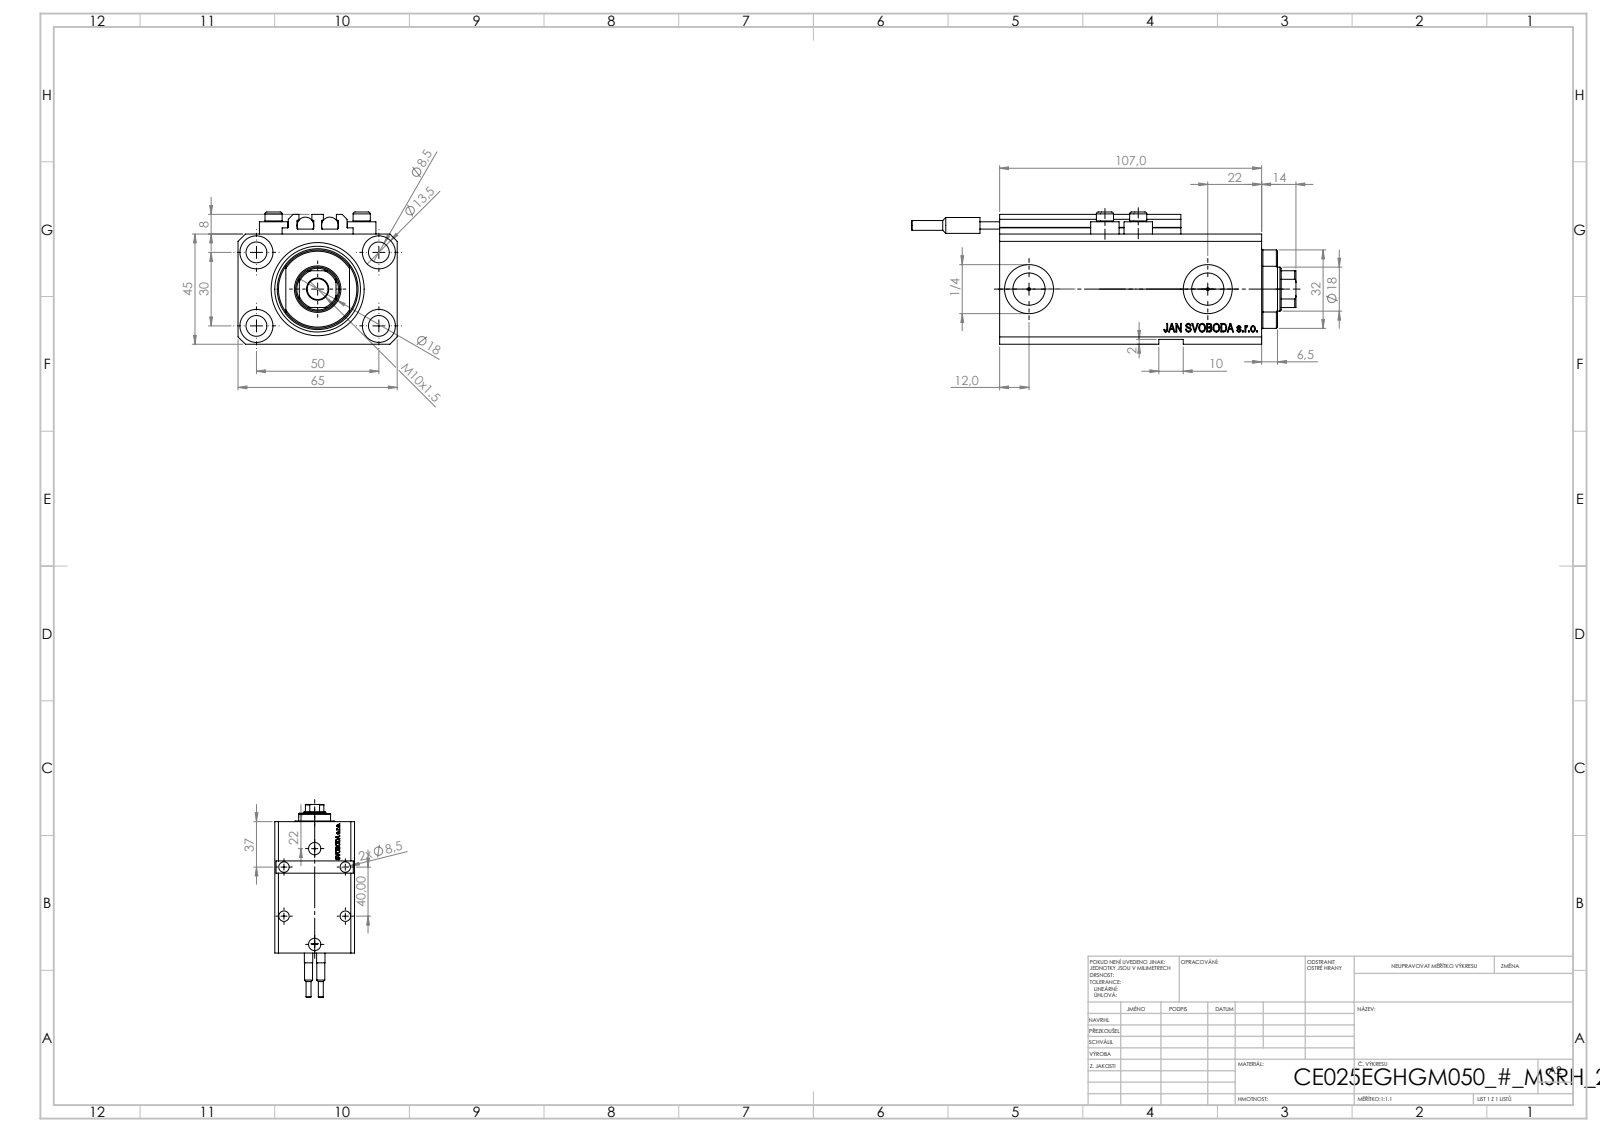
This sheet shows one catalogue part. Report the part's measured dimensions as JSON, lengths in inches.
{"part_name": "ALLEN BOLT V250CE; V250CE_C_VCP; SWITCH_V250CE; V250CE_VC_E (+1 more)", "step_written_by": "SolidWorks 2019 (CONFIG_CONTROL_DESIGN)", "units": "inches", "bodies": {"solids": 10, "faces": 1139, "planar": 543, "cylindrical": 158, "other": 438}, "overall_size": [6.181, 2.559, 2.126], "volume_in3": 16.9, "surface_area_in2": 123.4, "round_holes": [[0.335, 9], [0.049, 4], [0.157, 4], [0.531, 4], [0.394, 2], [0.518, 2], [0.787, 2], [0.709, 1], [0.984, 1], [1.496, 1]], "round_bosses_or_shafts": [[0.457, 4], [0.276, 4], [0.268, 2], [0.256, 2], [0.157, 2]], "partial_cylinders_radius": [[0.008, 10], [0.335, 1], [0.63, 1]], "face_to_face_distances": [1.772, 2.559, 0.079, 1.85, 3.661, 0.118, 0.551, 4.213, 0.394, 0.197], "hole_center_spacings": [1.148, 1.969, 0.535, 0.581, 0.595, 1.083, 1.098, 1.181]}
